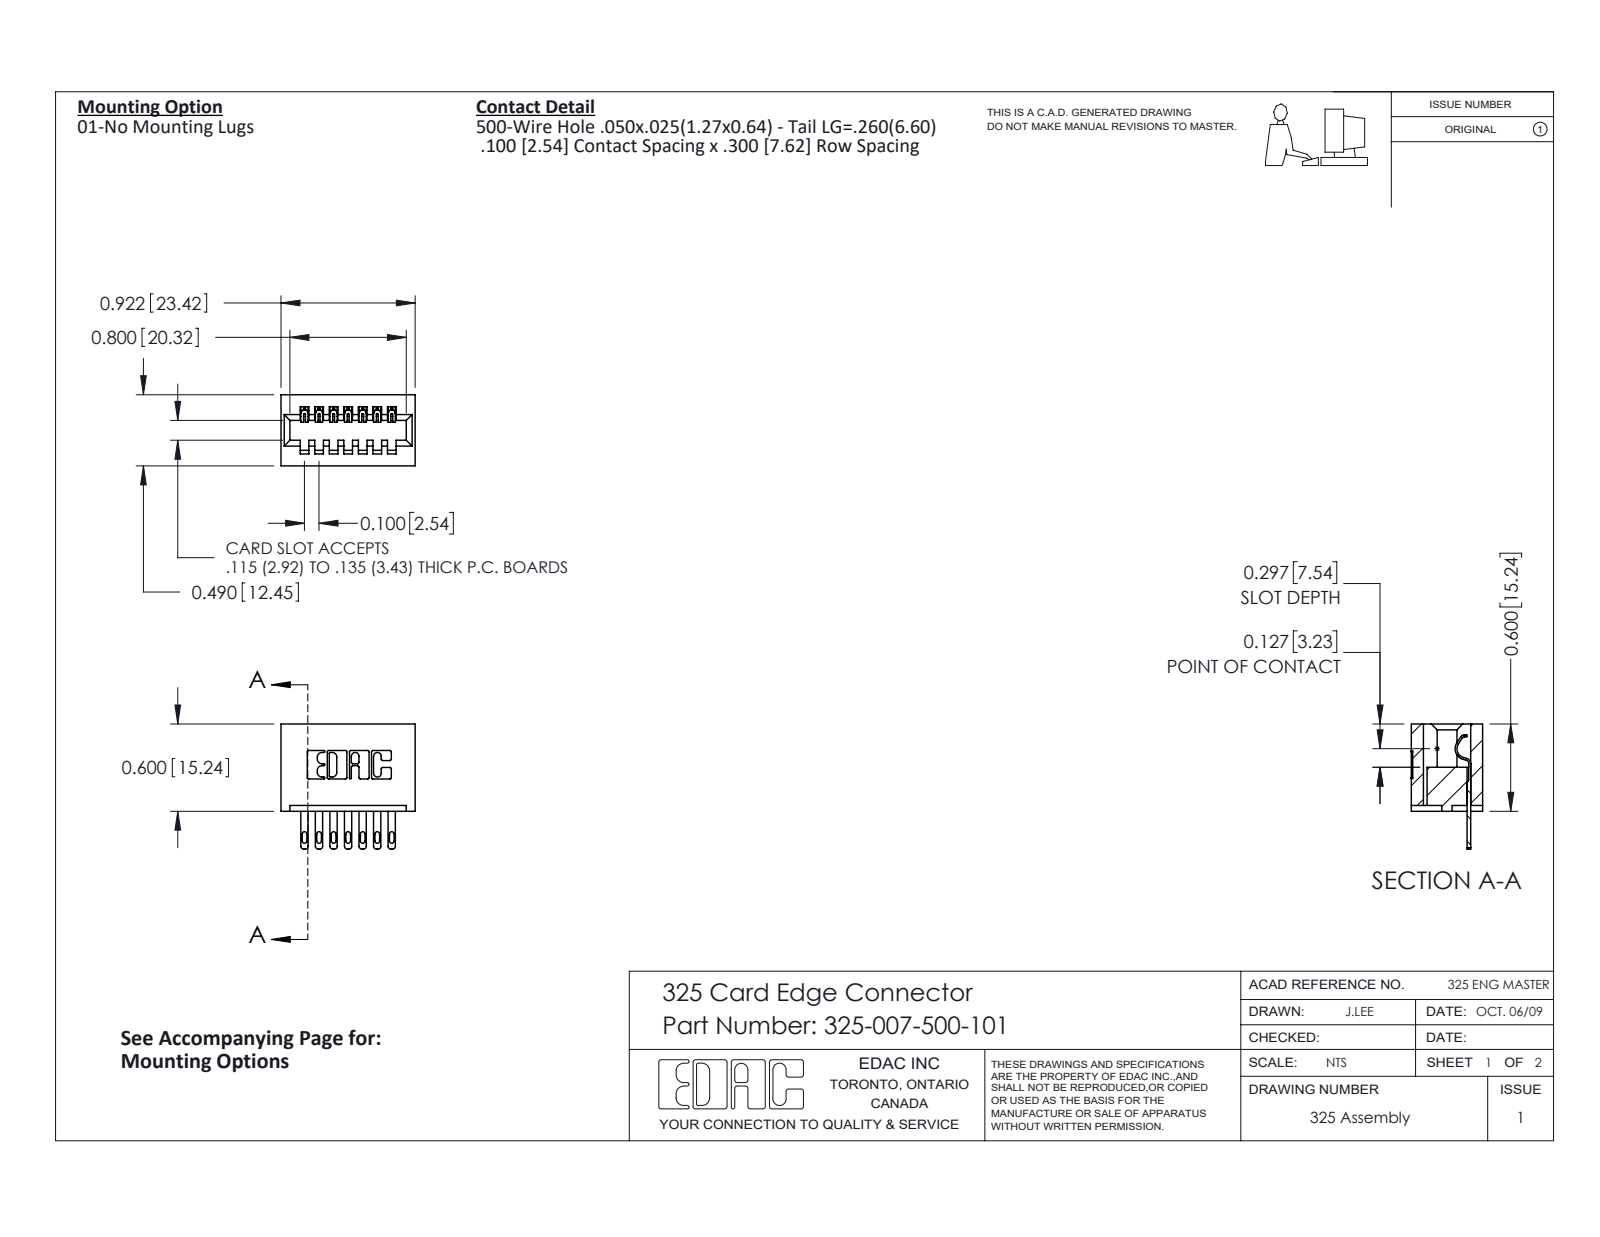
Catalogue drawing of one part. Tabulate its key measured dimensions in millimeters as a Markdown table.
| quantity | value |
| --- | --- |
| part name | 325 Part_Lugless; 325-007-500-101; 325-292-001_325-293-100 |
| STEP written by | SolidWorks 2016 (CONFIG_CONTROL_DESIGN) |
| units | millimeters |
| bodies | 8 solids, 484 faces (318 planar, 166 cylindrical, 0 other) |
| overall size | 23.4 × 21.8 × 12.4 |
| volume | 3 280 mm³ |
| surface area | 3 490 mm² |
| partial cylindrical surfaces (radius × count) | 0.3 × 22, 0.2 × 14, 0.4 × 14, 0.5 × 14, 0.2 × 6, 0.8 × 6, 0.7 × 3, 0.4 × 1 |
| main face-to-face distances | 7.6, 2.5, 5.1, 2.1, 10.3, 1, 1.5, 12.4, 4.1, 10.2 |
